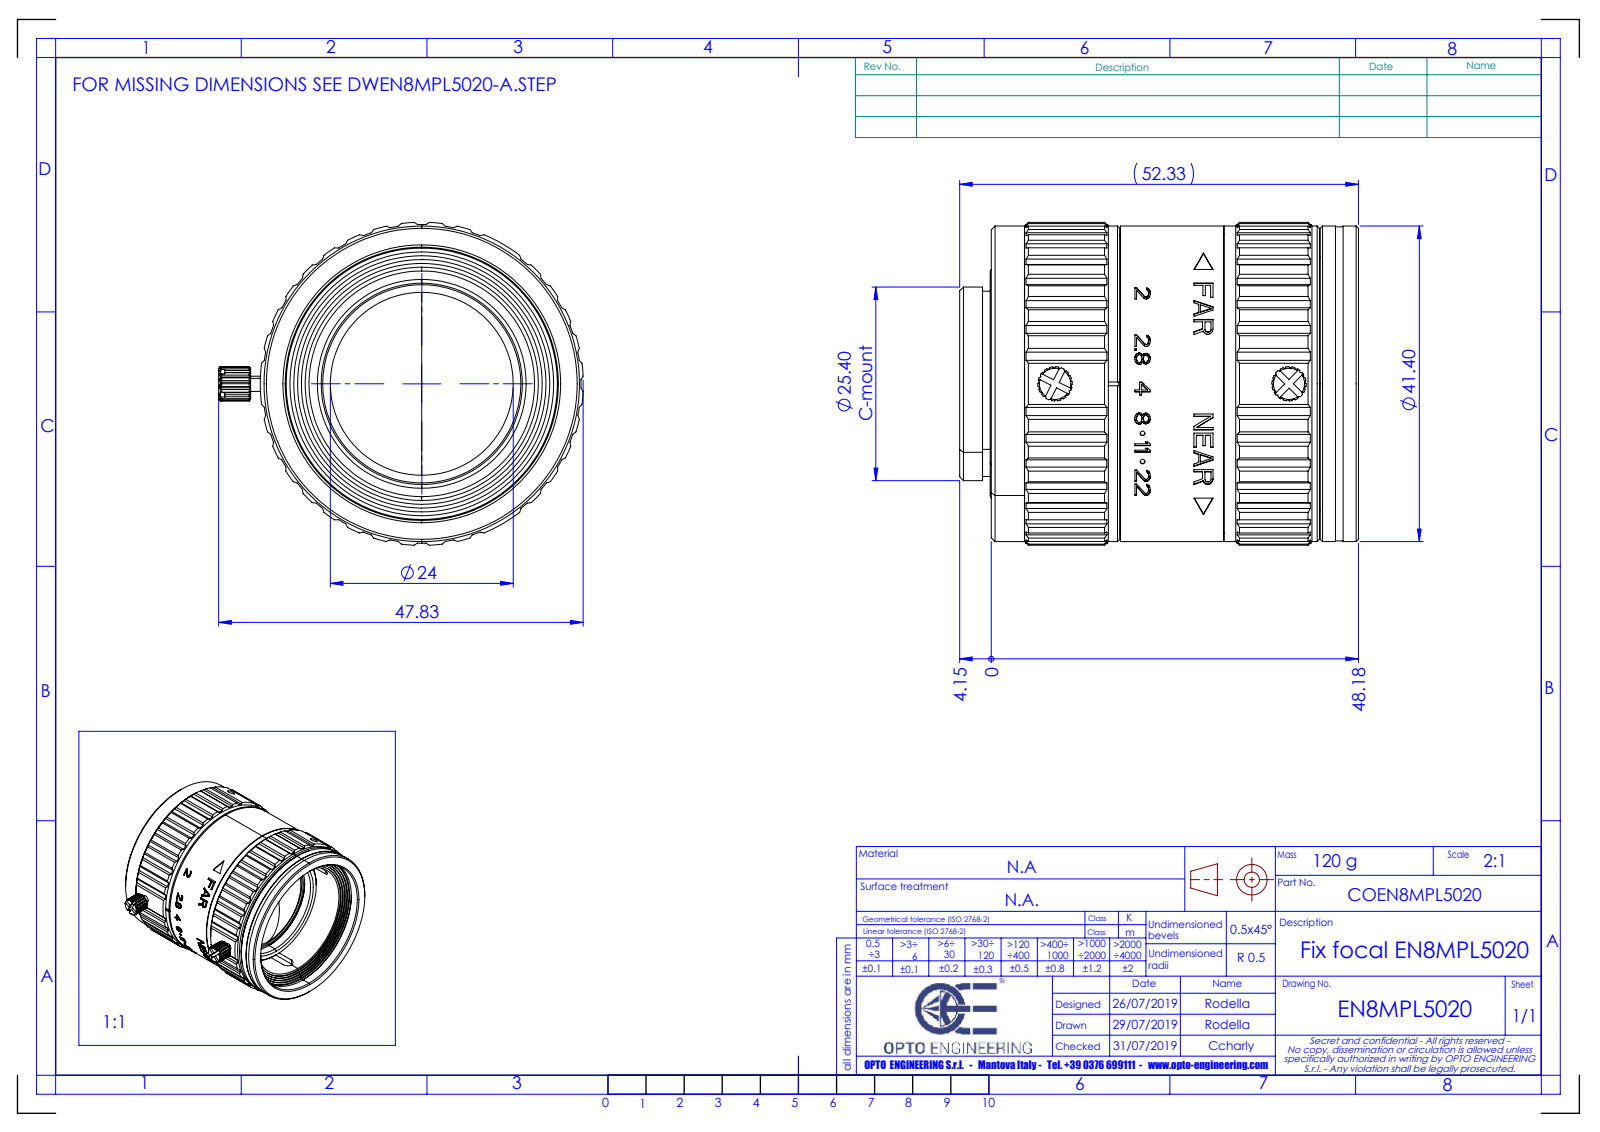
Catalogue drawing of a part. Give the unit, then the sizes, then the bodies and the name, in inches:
Units: inches
Overall size (bounding box): 2.06 × 1.883 × 1.667
Round holes (diameter × count): ⌀0.079 ×6, ⌀0.055 ×5, ⌀0.083 ×4, ⌀0.118 ×4, ⌀0.047 ×3, ⌀0.063 ×3, ⌀0.067 ×3, ⌀0.098 ×3, ⌀0.669 ×1, ⌀0.748 ×1, ⌀0.819 ×1, ⌀0.827 ×1
Round bosses / shafts (diameter × count): ⌀1.63 ×1, ⌀1.622 ×1, ⌀1.543 ×1, ⌀1.205 ×1, ⌀1.15 ×1, ⌀1.067 ×1, ⌀1 ×1, ⌀0.961 ×1
Partial cylindrical surfaces — rounded edges, fillets, slot ends (radius × count): R0.059 ×6, R0.02 ×4, R0.053 ×3, R0.028 ×2, R0.039 ×2, R0.047 ×2, R0.089 ×2, R0.467 ×1
Main face-to-face distances: 0.067, 0.191, 0.337, 0.258, 1.442, 1.633, 1.7, 1.552, 0.11, 0.081
Hole centre spacings: 0.65, 0.919, 0.492, 1.209, 0.119, 0.216, 0.45, 0.461
Volume: 1.843 in³ · Surface area: 57.17 in²
Bodies: 10 solids, 1463 faces (729 planar, 404 cylindrical, 330 other)
Part name (STEP PRODUCT): EN8MPL5020-03; EN8MPL5020-04; EN8MPL5020-06; EN8MPL5020-07 (+8 more)
STEP written by: PRO/ENGINEER BY PARAMETRIC TECHNOLOGY CORPORATION, 2015240 (CONFIG_CONTROL_DESIGN)
